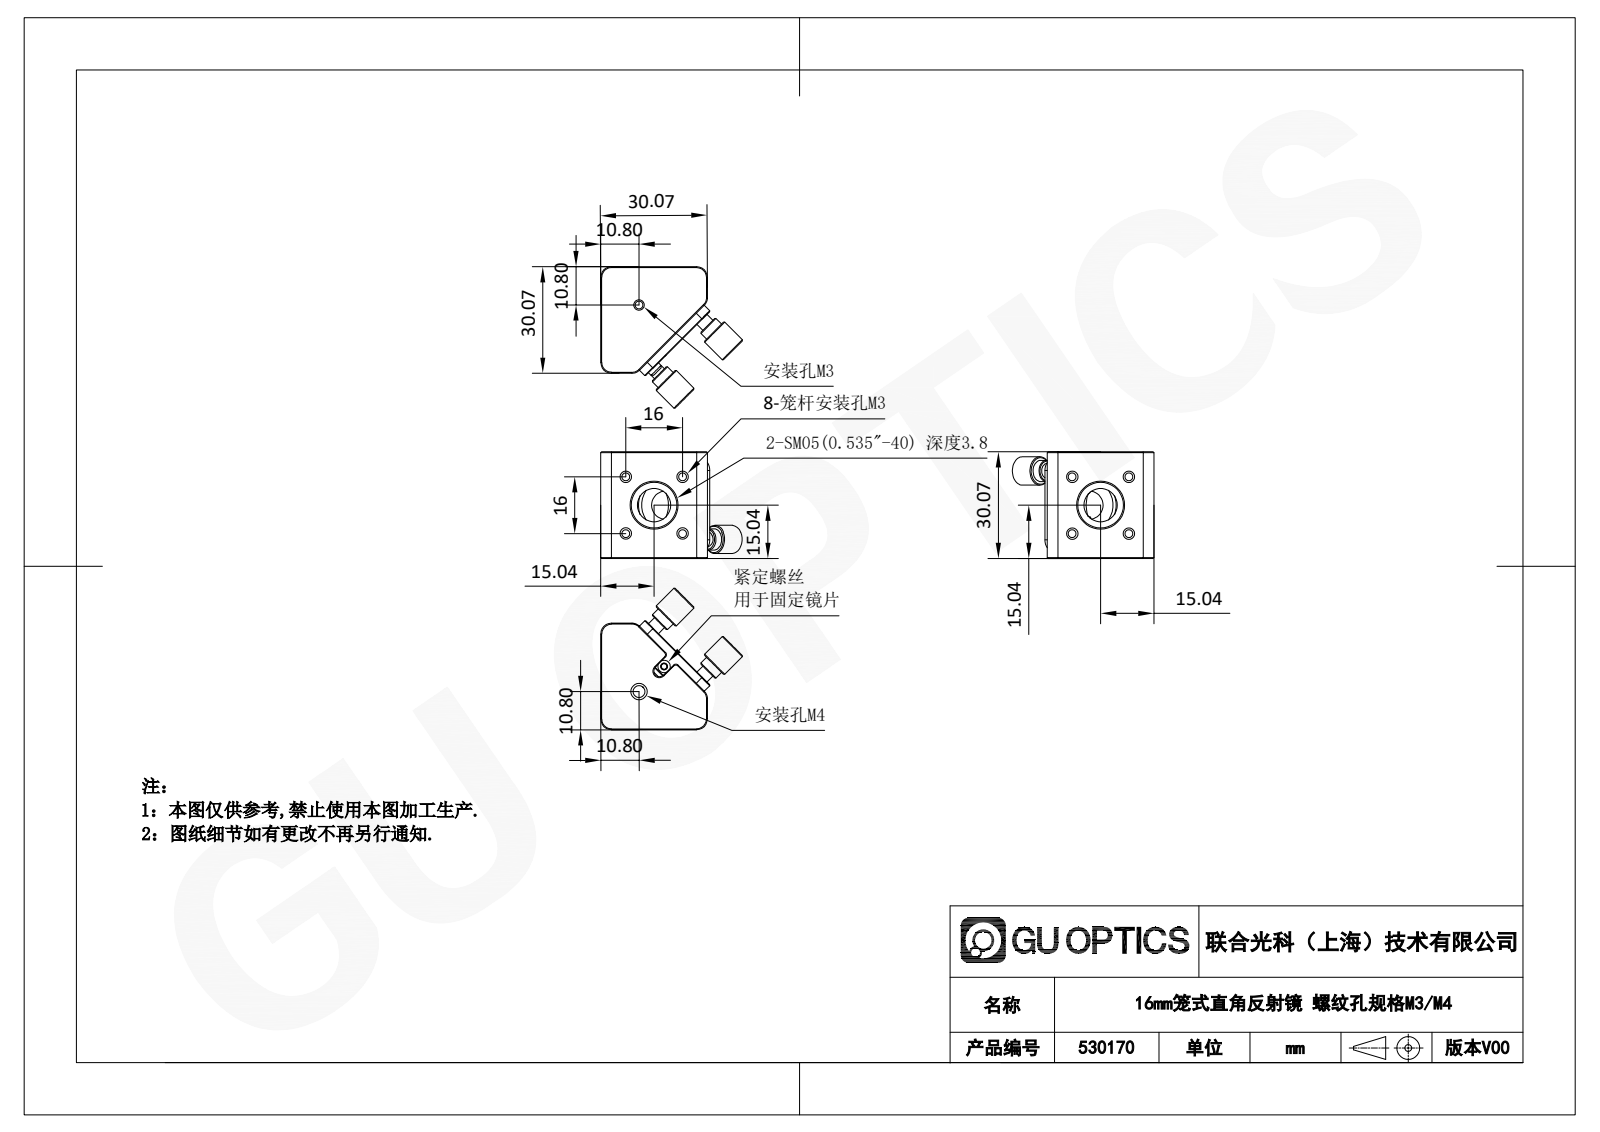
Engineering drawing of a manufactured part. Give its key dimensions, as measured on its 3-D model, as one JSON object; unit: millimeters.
{"part_name": "530170", "step_written_by": "SolidWorks 2020 (CONFIG_CONTROL_DESIGN)", "units": "millimeters", "bodies": {"solids": 16, "faces": 365, "planar": 159, "cylindrical": 90, "other": 116}, "overall_size": [40.62, 40.62, 30.07], "volume_mm3": 16624, "surface_area_mm2": 11262, "round_holes": [[2.5, 10], [3.5, 6], [3.75, 5], [2.9, 4], [2.99, 3], [9.5, 2], [12.95, 2], [13.95, 2], [3.3, 1], [4.6, 1], [11.94, 1], [18, 1]], "round_bosses_or_shafts": [[4, 3], [1.5, 3], [8, 2], [6, 2], [3, 2], [16.5, 1], [2, 1]], "partial_cylinders_radius": [[0.78, 12], [3, 9], [1, 4], [3.17, 4], [0.3, 2], [4, 2], [1.59, 1], [1.75, 1]], "face_to_face_distances": [30.08, 0.75, 26.65, 10.62, 3, 7.62, 1.34, 28.74, 27.4, 2.09], "hole_center_spacings": [11.31, 16, 4.85, 14.45, 22.63, 13.64, 19.3, 19.9]}
